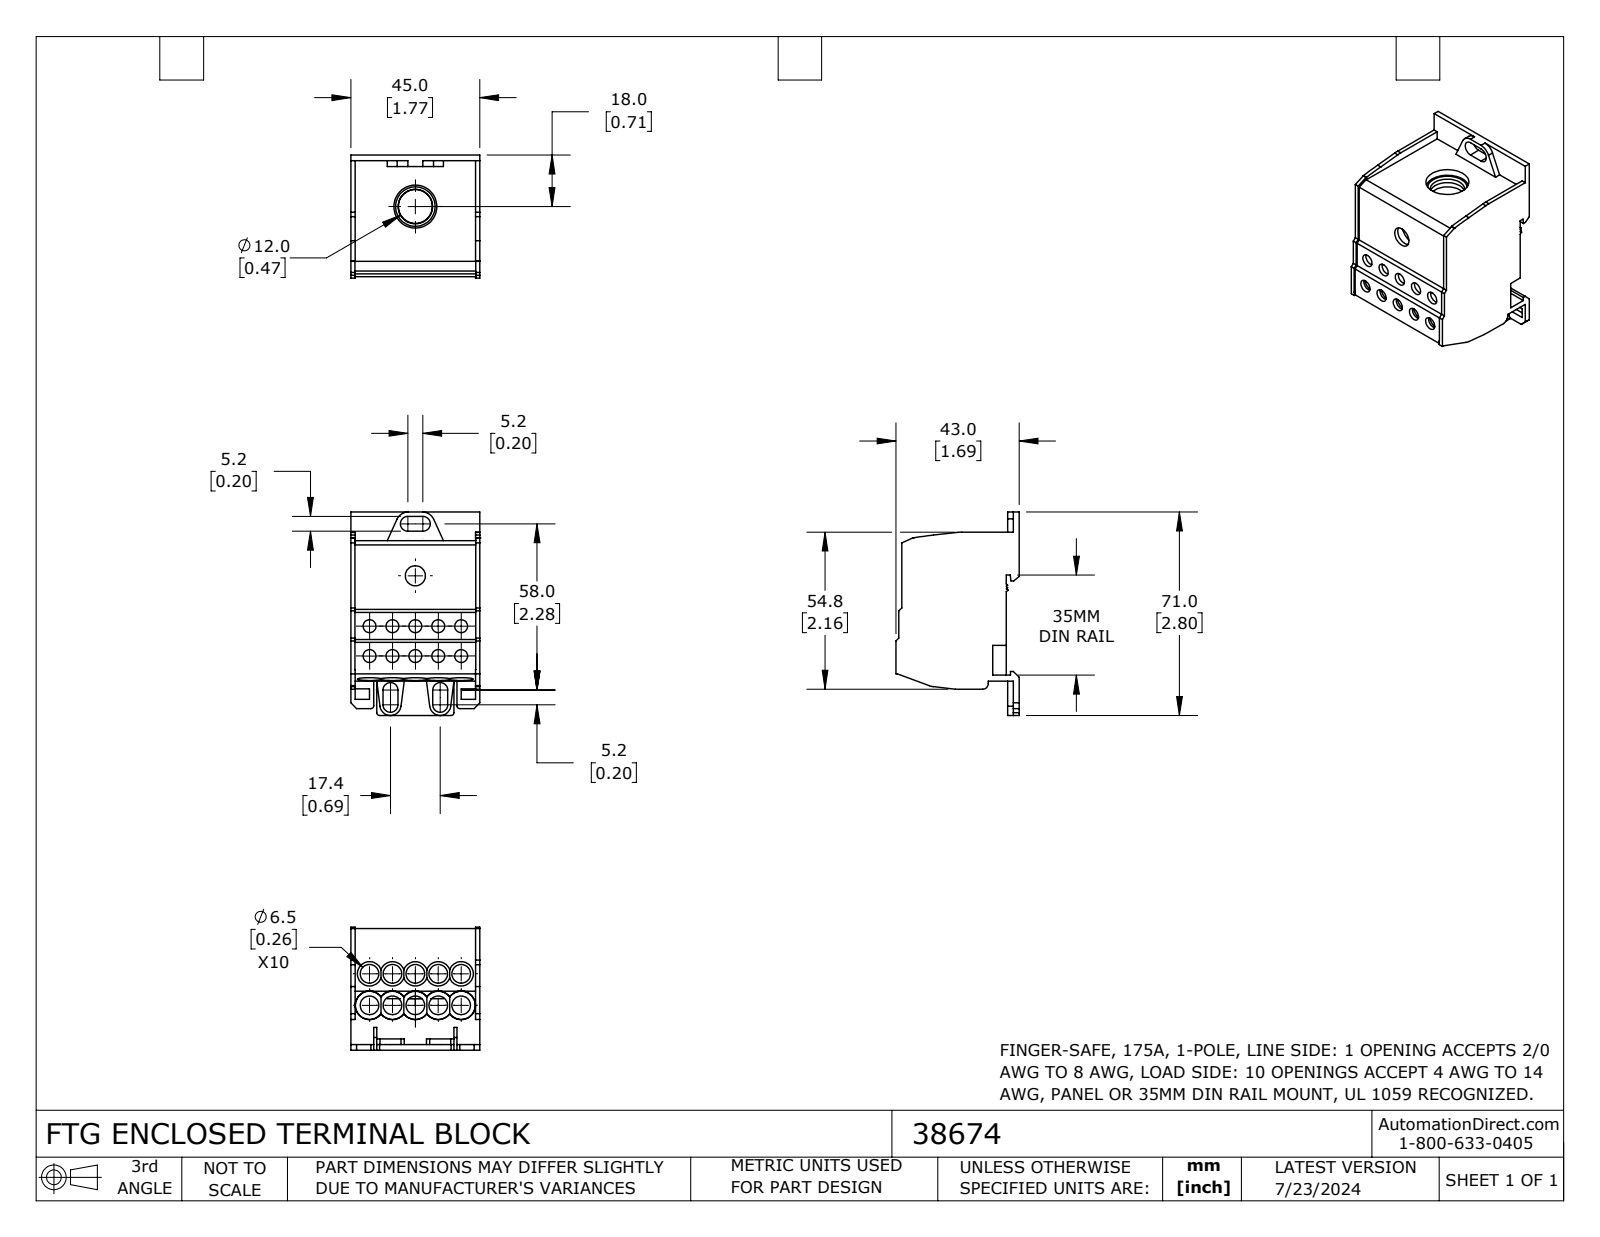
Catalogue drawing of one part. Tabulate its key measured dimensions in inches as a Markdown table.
| quantity | value |
| --- | --- |
| part name | 38674 |
| STEP written by | SolidWorks 2023 (CONFIG_CONTROL_DESIGN) |
| units | inches |
| bodies | 1 solid, 361 faces (194 planar, 121 cylindrical, 46 other) |
| overall size | 2.795 × 1.772 × 1.693 |
| volume | 4.243 in³ |
| surface area | 35.34 in² |
| round holes (diameter × count) | 0.256 × 20, 0.177 × 10, 0.335 × 2, 0.394 × 2, 0.276 × 1, 0.433 × 1, 0.466 × 1, 0.472 × 1, 0.584 × 1, 0.591 × 1 |
| partial cylindrical surfaces (radius × count) | 0.102 × 6, 0.187 × 5, 0.039 × 4, 0.167 × 3, 0.197 × 3, 0.146 × 2, 0.161 × 2, 0.079 × 1 |
| main face-to-face distances | 1.772, 0.177, 0.079, 1.594, 1.417, 0.039, 0.059, 0.02, 1.457, 1.516 |
| hole center spacings | 0.315, 0.63, 0.517, 0.535, 0.945, 0.751, 0.765, 0.409 |
